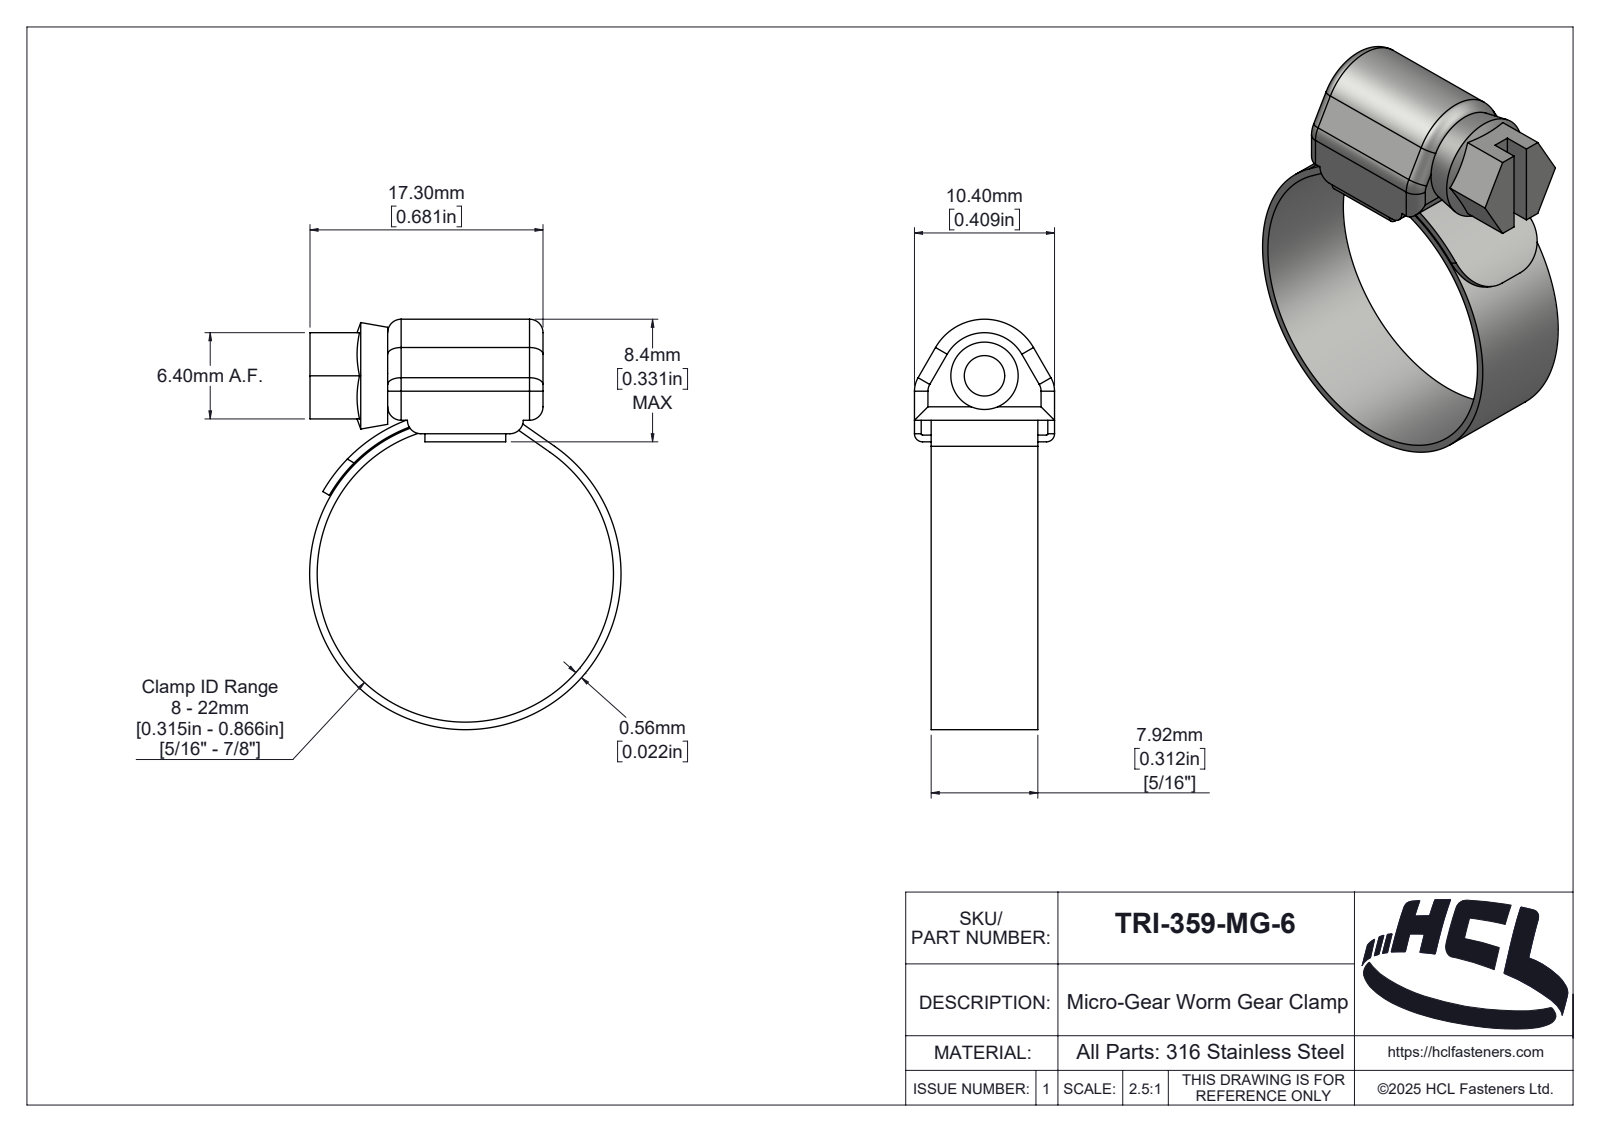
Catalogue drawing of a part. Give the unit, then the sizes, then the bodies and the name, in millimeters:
Units: millimetres
Overall size (bounding box): 27.46 × 21.59 × 10.4
Round holes (diameter × count): ⌀5 ×1, ⌀19 ×1
Round bosses / shafts (diameter × count): ⌀20.12 ×1
Partial cylindrical surfaces — rounded edges, fillets, slot ends (radius × count): R1 ×12, R2 ×3, R0.1 ×2, R0.6 ×2, R3 ×2, R0.25 ×1, R1.01 ×1, R1.26 ×1
Main face-to-face distances: 1.1, 0.5, 1.24, 9.16, 1.6, 7.92, 6.2, 10.4, 0.56, 5.76
Volume: 1 264 mm³ · Surface area: 2 399 mm²
Bodies: 3 solids, 186 faces (38 planar, 87 cylindrical, 61 other)
Part name (STEP PRODUCT): TRI-359-MG-6
STEP written by: SolidWorks 2025 (AUTOMOTIVE_DESIGN)
